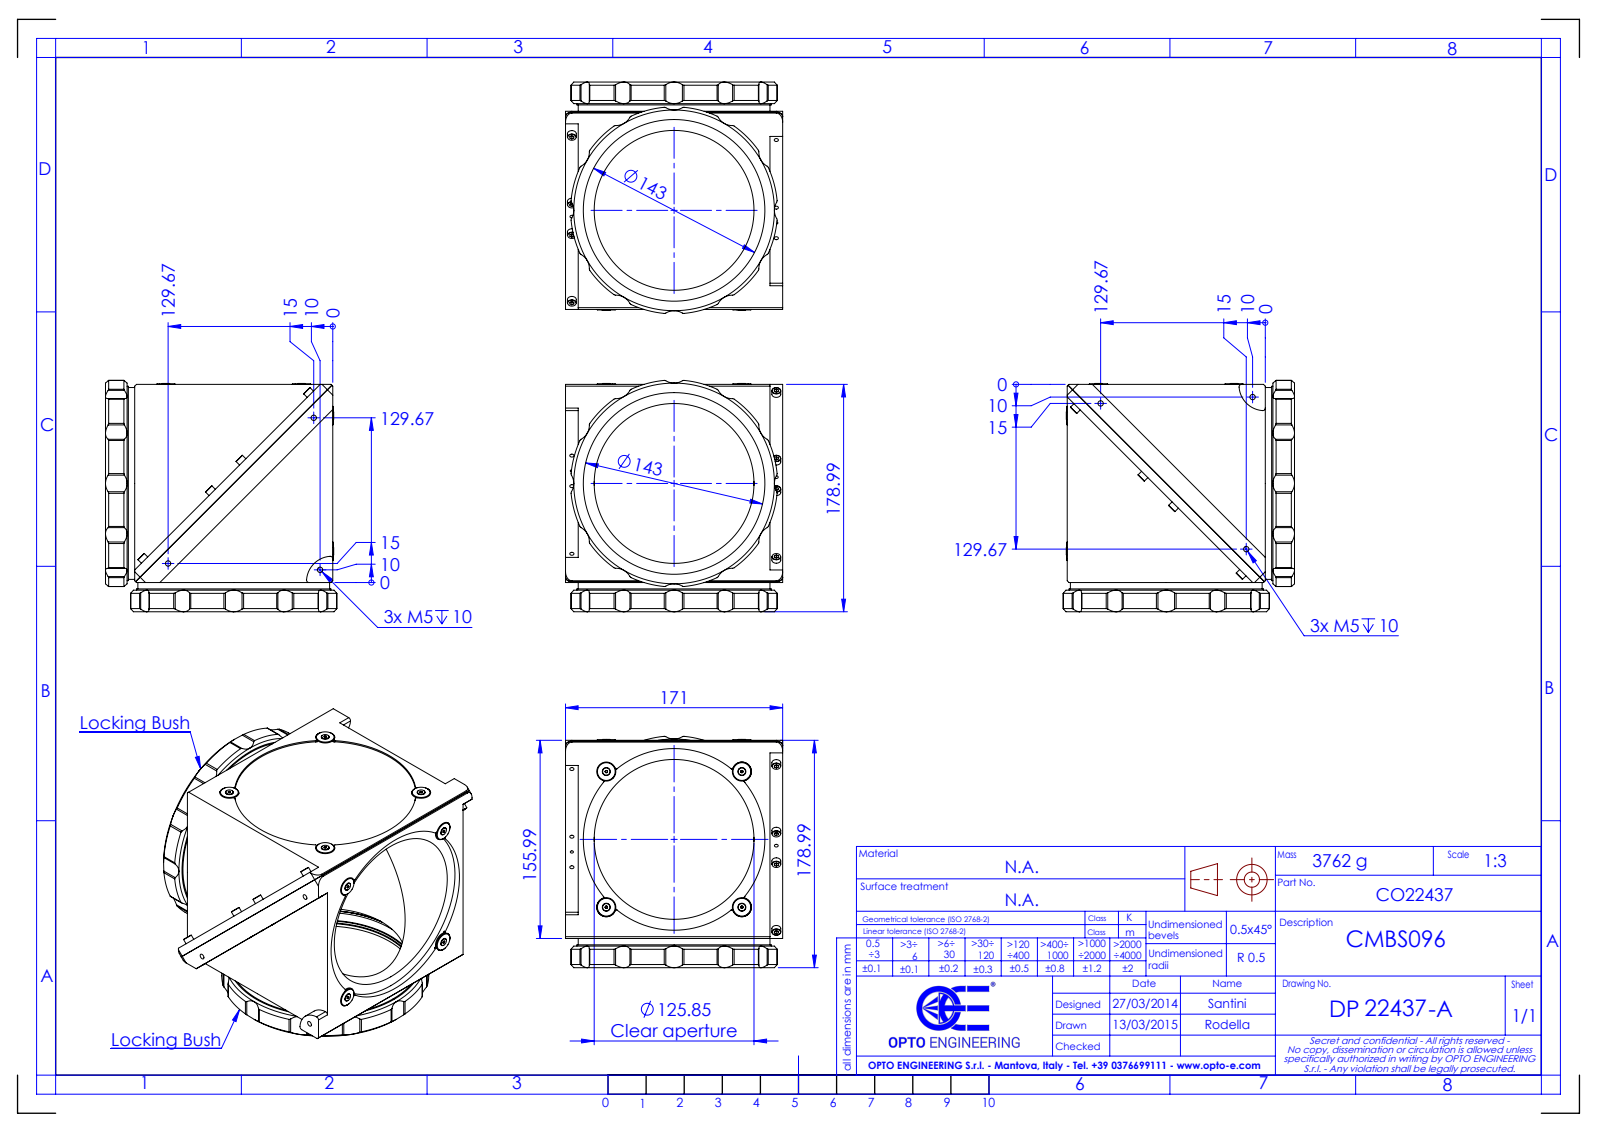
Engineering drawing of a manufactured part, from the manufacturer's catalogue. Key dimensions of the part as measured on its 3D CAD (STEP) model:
Part name (STEP PRODUCT): DP22437-A_CMBS096
STEP written by: SolidWorks 2021 (CONFIG_CONTROL_DESIGN)
Units: millimetres
Bodies: 0 solids, 582 faces (147 planar, 297 cylindrical, 138 other)
Overall size (bounding box): 182.13 × 182.13 × 171
Round holes (diameter × count): ⌀3.3 ×8, ⌀4.2 ×6, ⌀15 ×3, ⌀2.5 ×2, ⌀3 ×2, ⌀125.85 ×2, ⌀143 ×2, ⌀143.6 ×2, ⌀145.2 ×2, ⌀147.5 ×2, ⌀151 ×2, ⌀153 ×1
Round bosses / shafts (diameter × count): ⌀7 ×8, ⌀5.75 ×8, ⌀15 ×5, ⌀153 ×1, ⌀142.6 ×1
Partial cylindrical surfaces — rounded edges, fillets, slot ends (radius × count): R2 ×52, R12.5 ×24, R1 ×16, R5 ×4, R20 ×2, R81.5 ×2
Main face-to-face distances: 2, 151, 4, 5, 155.98, 150.98, 10, 154.98, 161, 1
Hole centre spacings: 161, 17, 75.31, 92.31, 109.3, 119.77, 131.99, 161.89
